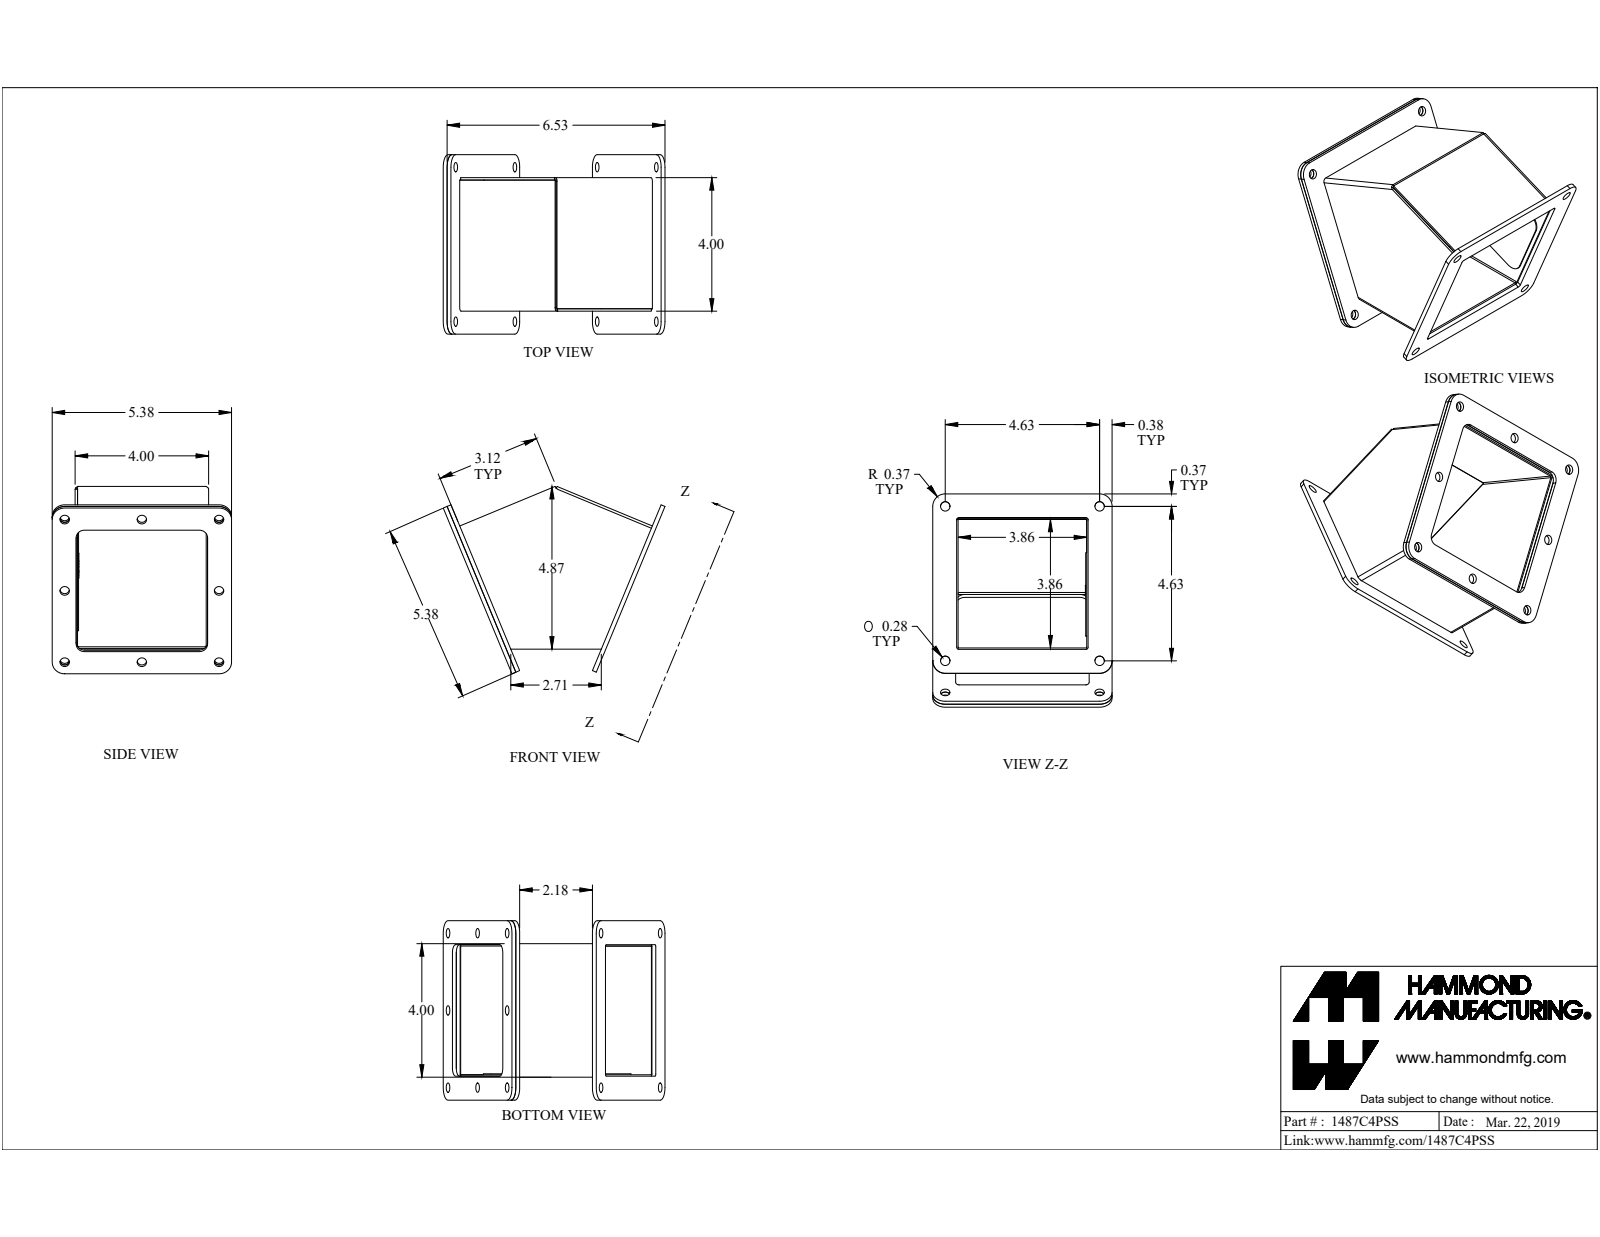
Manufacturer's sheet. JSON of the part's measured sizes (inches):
{"part_name": "1487C4PSS", "step_written_by": "SolidWorks 2019 (CONFIG_CONTROL_DESIGN)", "units": "inches", "bodies": {"solids": 8, "faces": 270, "planar": 165, "cylindrical": 74, "other": 31}, "overall_size": [6.776, 5.611, 5.375], "volume_in3": 10.41, "surface_area_in2": 262.3, "round_holes": [[0.281, 12], [0.196, 1], [0.258, 1], [0.35, 1]], "round_bosses_or_shafts": [[0.5, 1], [0.25, 1]], "partial_cylinders_radius": [[0.375, 12], [0.02, 6], [0.062, 6], [0.036, 4], [0.108, 4], [0.25, 4], [0.063, 2]], "face_to_face_distances": [0.072, 3.928, 0.125, 3.856, 4, 0.124, 0.125, 0.249, 0.124, 0.03], "hole_center_spacings": [2.313, 4.625, 5.171, 3.27, 6.541, 4.625, 2.31, 2.311]}
